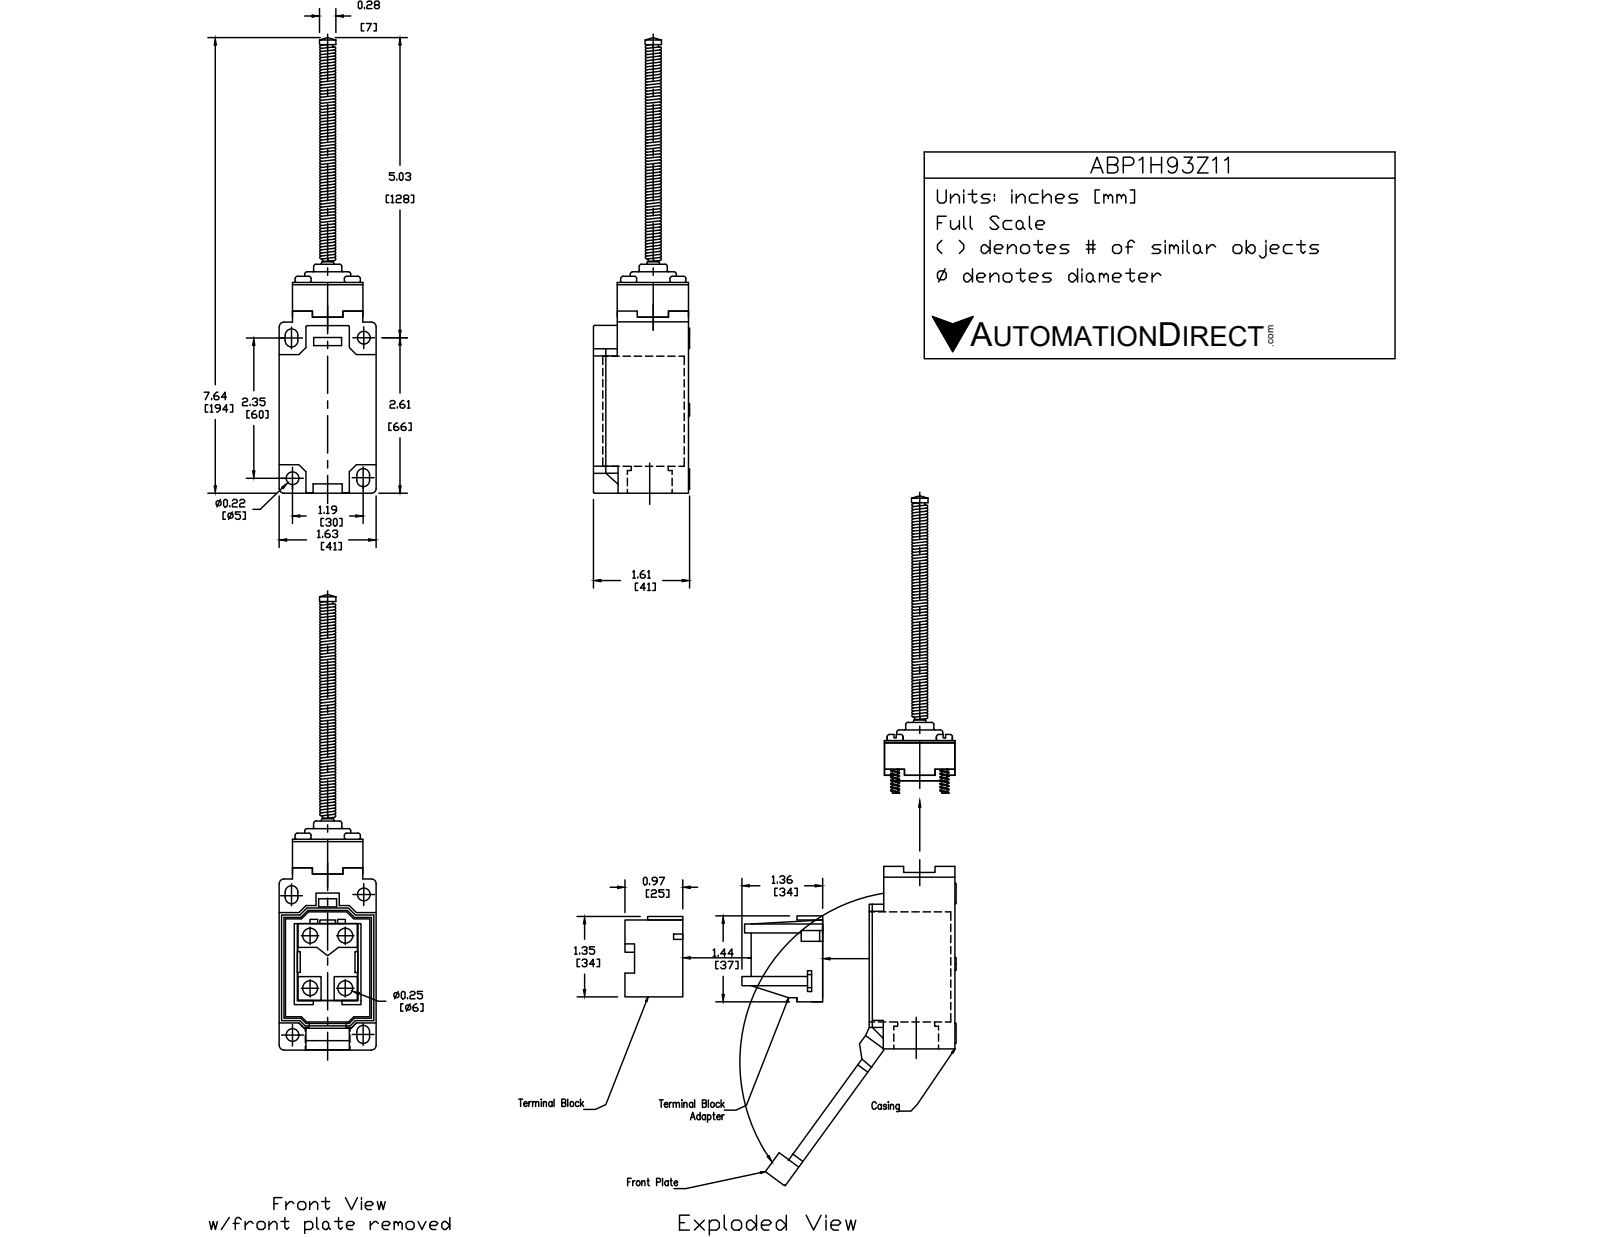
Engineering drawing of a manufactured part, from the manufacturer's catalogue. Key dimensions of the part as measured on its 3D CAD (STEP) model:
Part name (STEP PRODUCT): ABP1H93Z11
STEP written by: SolidWorks 2017 (AUTOMOTIVE_DESIGN)
Units: inches
Bodies: 3 solids, 188 faces (80 planar, 76 cylindrical, 32 other)
Overall size (bounding box): 7.638 × 1.614 × 1.585
Volume: 7.82 in³ · Surface area: 38.01 in²
Round holes (diameter × count): ⌀0.213 ×2, ⌀0.669 ×1, ⌀0.748 ×1, ⌀0.807 ×1
Round bosses / shafts (diameter × count): ⌀0.276 ×5, ⌀0.354 ×4, ⌀0.748 ×1, ⌀0.461 ×1, ⌀0.268 ×1
Partial cylindrical surfaces — rounded edges, fillets, slot ends (radius × count): R0.02 ×16, R0.024 ×4, R0.079 ×4, R0.106 ×4, R0.453 ×1, R0.472 ×1
Main face-to-face distances: 1.614, 1.565, 1.181, 2.972, 1.398, 0.384, 0.217, 3.071, 0.098, 0.472
Hole centre spacings: 0.059, 2.641
